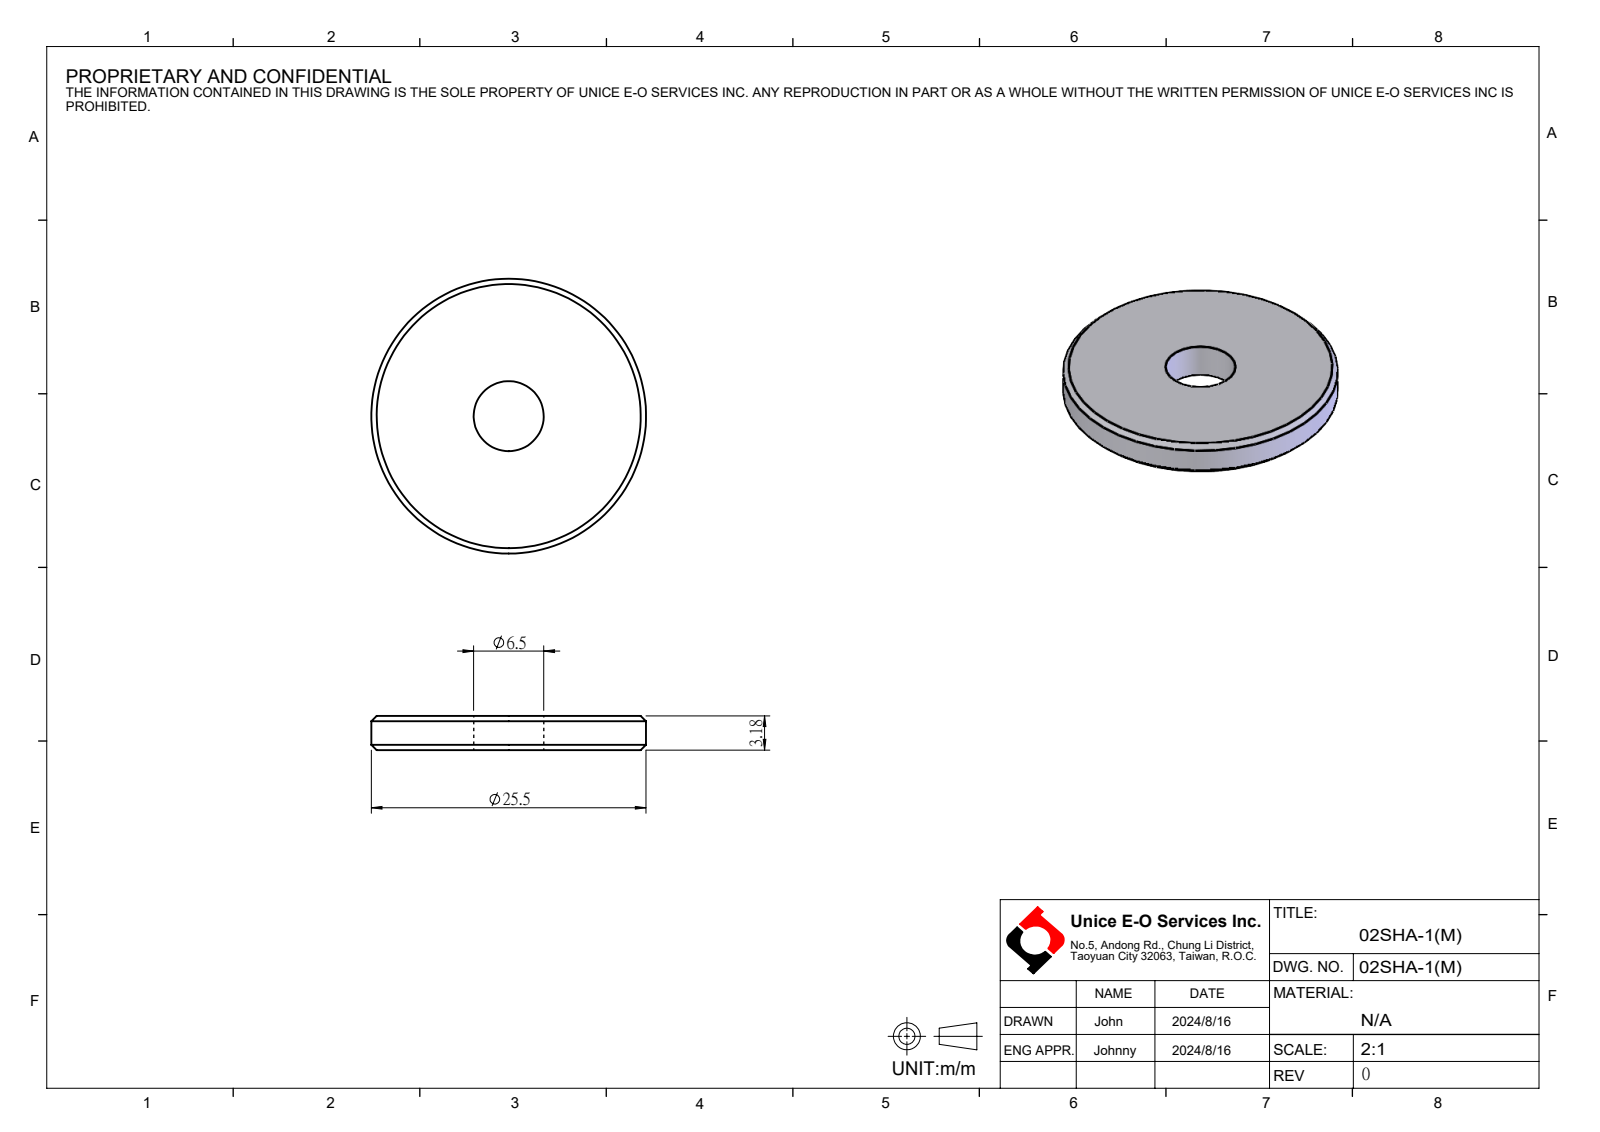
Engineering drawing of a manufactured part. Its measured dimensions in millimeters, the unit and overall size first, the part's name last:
Units: millimetres
Overall size (bounding box): 25.5 × 25.5 × 3.18
Round holes (diameter × count): ⌀6.5 ×1
Round bosses / shafts (diameter × count): ⌀25.5 ×1
Main face-to-face distances: 3.18
Volume: 1 499 mm³ · Surface area: 1 227 mm²
Bodies: 1 solid, 10 faces (2 planar, 4 cylindrical, 4 other)
Part name (STEP PRODUCT): 02SHA-1(M)
STEP written by: SolidWorks 2024 (CONFIG_CONTROL_DESIGN)
